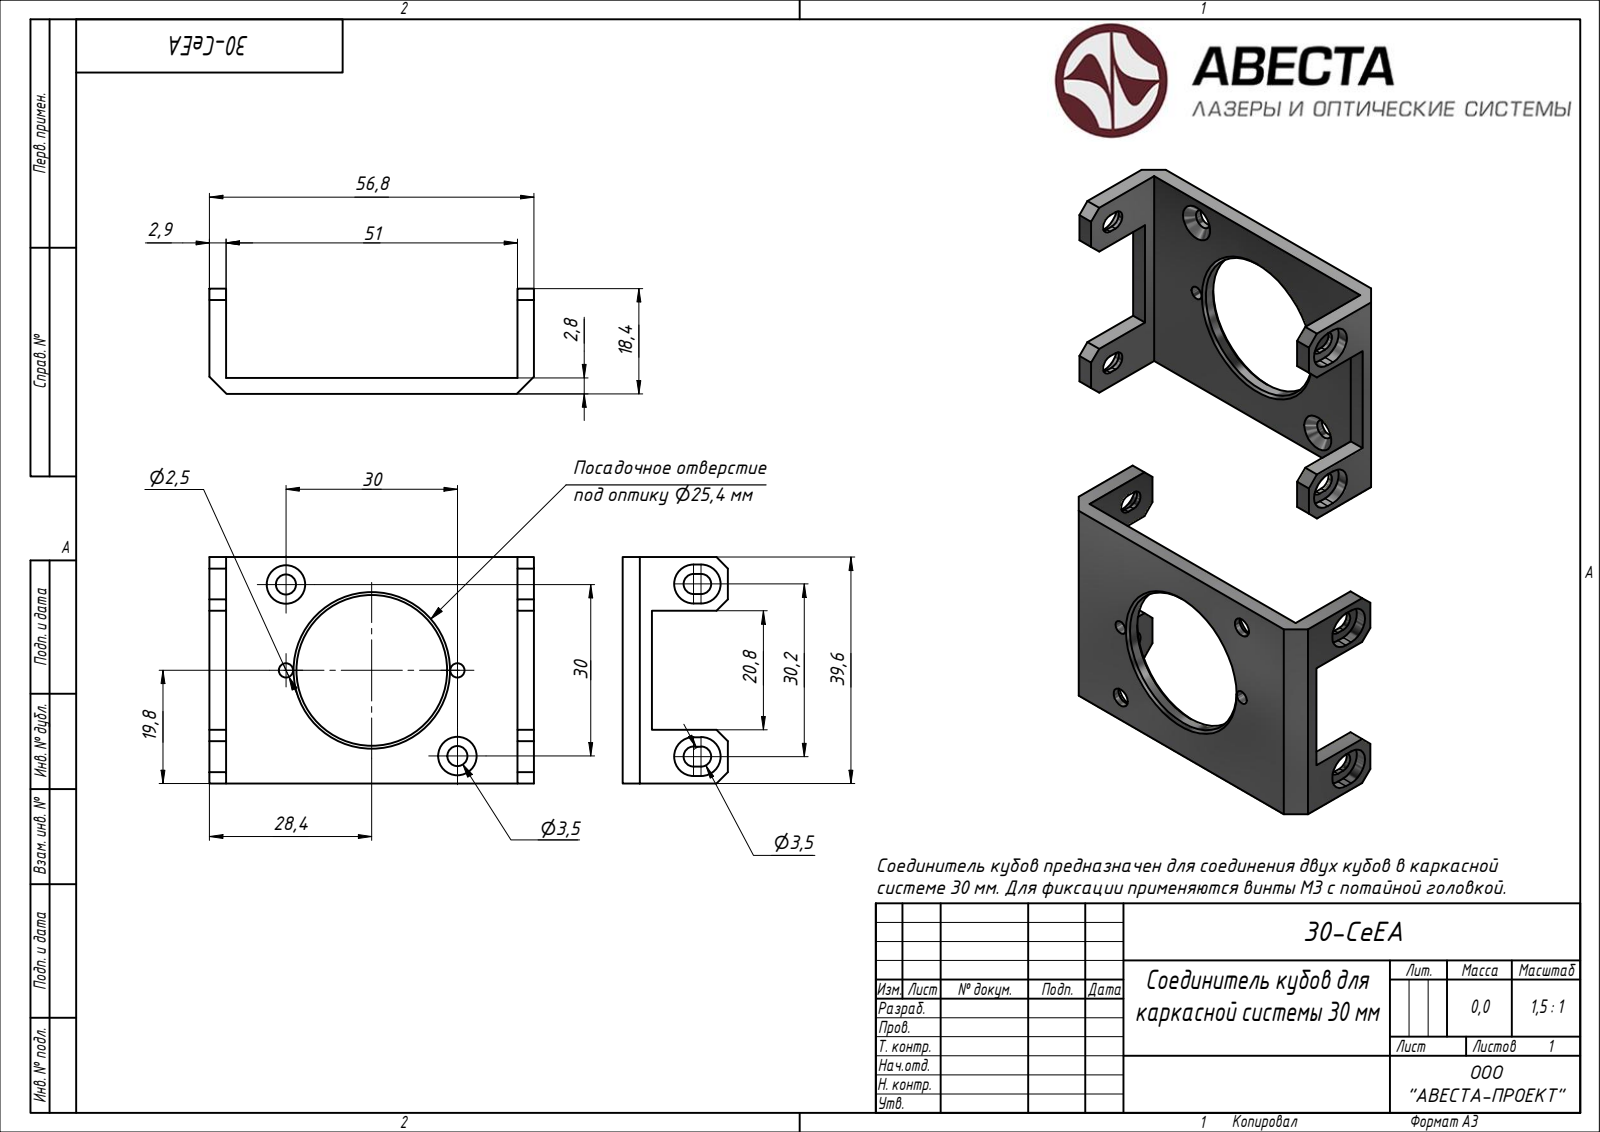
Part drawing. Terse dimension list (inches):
name: 30-CeEA
written by: Autodesk Inventor 2020 (AUTOMOTIVE_DESIGN)
unit: in
bodies: 1 solid, 73 faces (48 planar, 21 cylindrical, 4 other)
size: 2.236 × 1.559 × 0.724
volume: 0.353 in³; area: 8.947 in²
holes: 2× ⌀0.098, 2× ⌀0.138, 1× ⌀1.039
rounds: 4× R0.069, 4× R0.134
face distances: 0.11, 0.114, 2.122, 2.008, 2.236, 1.559, 1.189, 0.37, 0.079, 2.157
hole spacings: 0.591, 0.835, 1.32, 1.181, 1.67
